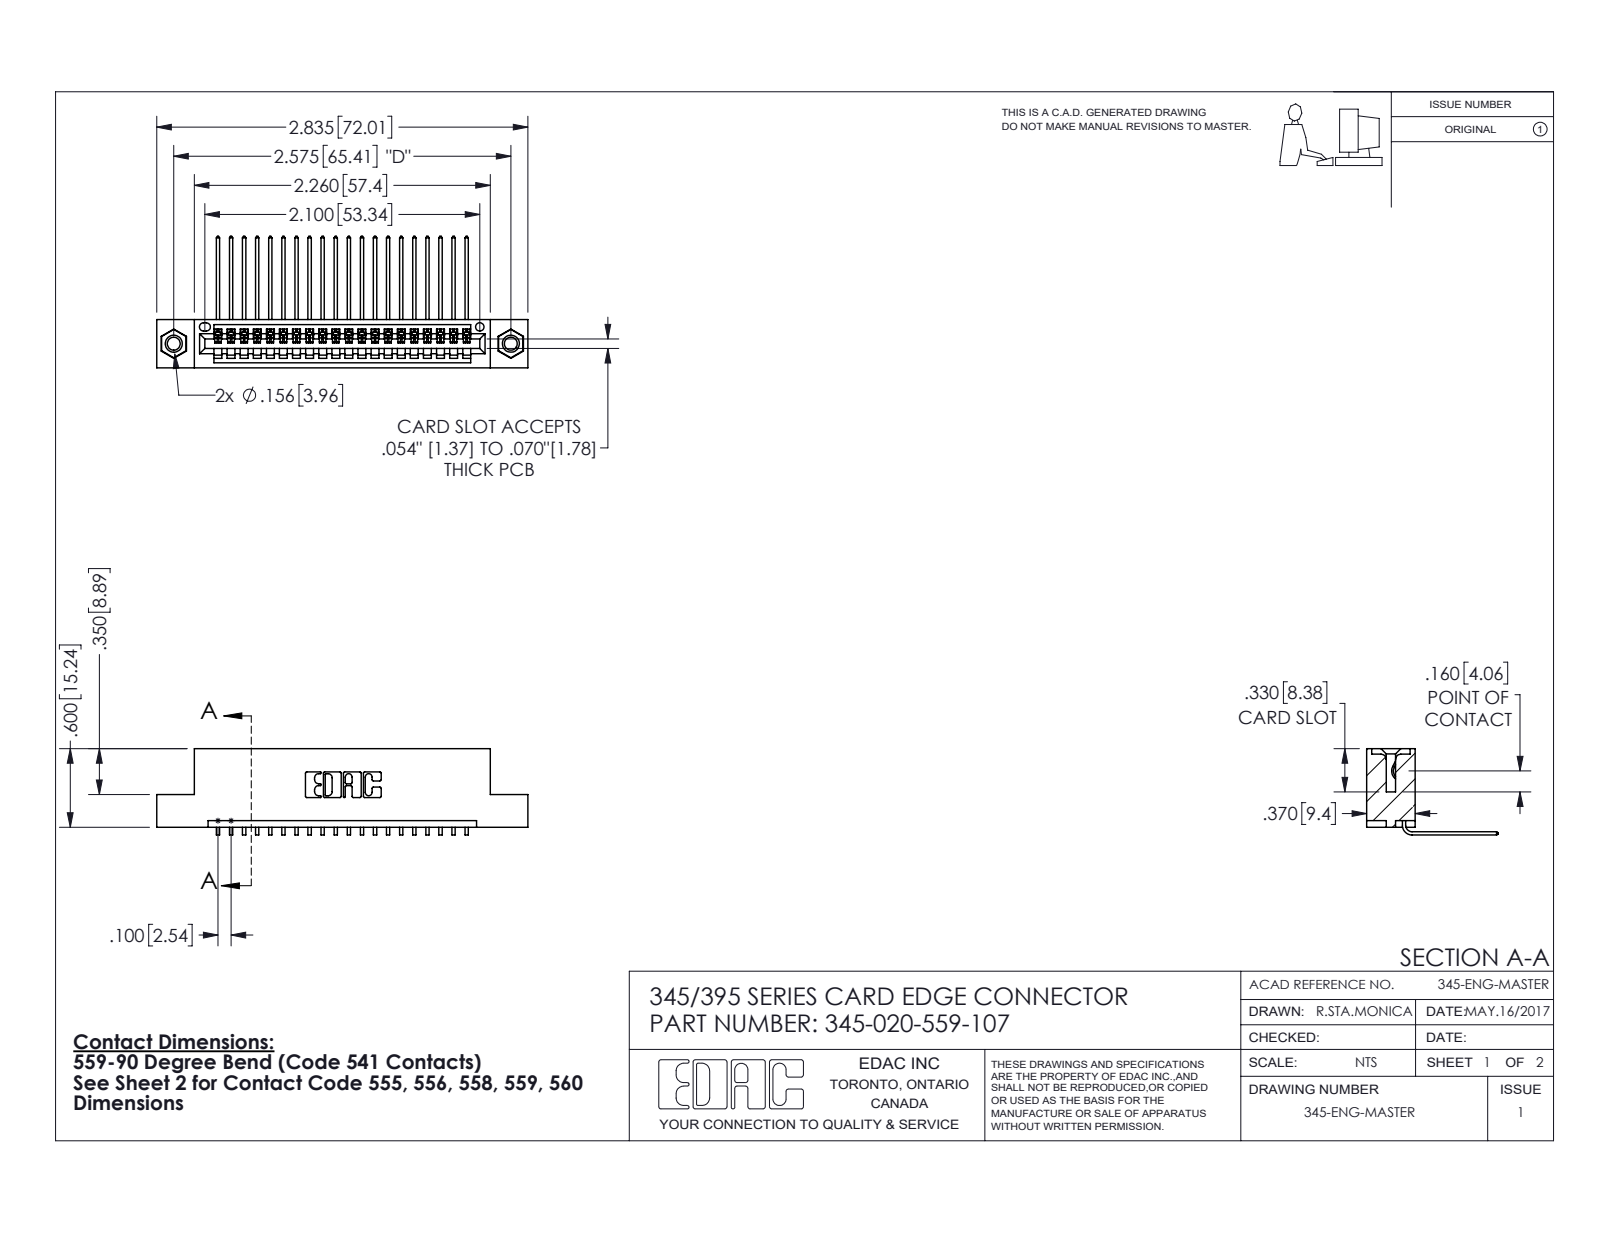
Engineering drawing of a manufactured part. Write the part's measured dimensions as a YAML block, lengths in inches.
part_name: "345-292-001_558 559 Tail - 1; 345-250-001_345-250-005-103; 345-020-559-107; 345 Part_Flush Mounting Lugs - 0.156 Dia-TI"
step_written_by: "SolidWorks 2016 (CONFIG_CONTROL_DESIGN)"
units: inches
bodies: {solids: 23, faces: 1386, planar: 952, cylindrical: 418, other: 16}
overall_size: [2.835, 1.005, 0.659]
volume: 0.41
surface_area: 14.02
round_holes:
  - {diameter: 0.098, count: 2}
  - {diameter: 0.125, count: 2}
  - {diameter: 0.156, count: 2}
  - {diameter: 0.064, count: 1}
round_bosses_or_shafts:
  - {diameter: 0.155, count: 2}
partial_cylinders:
  - {radius: 0.006, count: 40}
  - {radius: 0.01, count: 22}
  - {radius: 0.007, count: 6}
  - {radius: 0.031, count: 6}
  - {radius: 0.026, count: 3}
  - {radius: 0.031, count: 2}
  - {radius: 0.04, count: 2}
  - {radius: 0.014, count: 1}
face_to_face_distances: [0.072, 0.298, 0.2, 0.37, 0.098, 0.272, 0.025, 0.225, 0.149, 0.6]
hole_center_spacings: [0.27, 2.341, 2.575]
